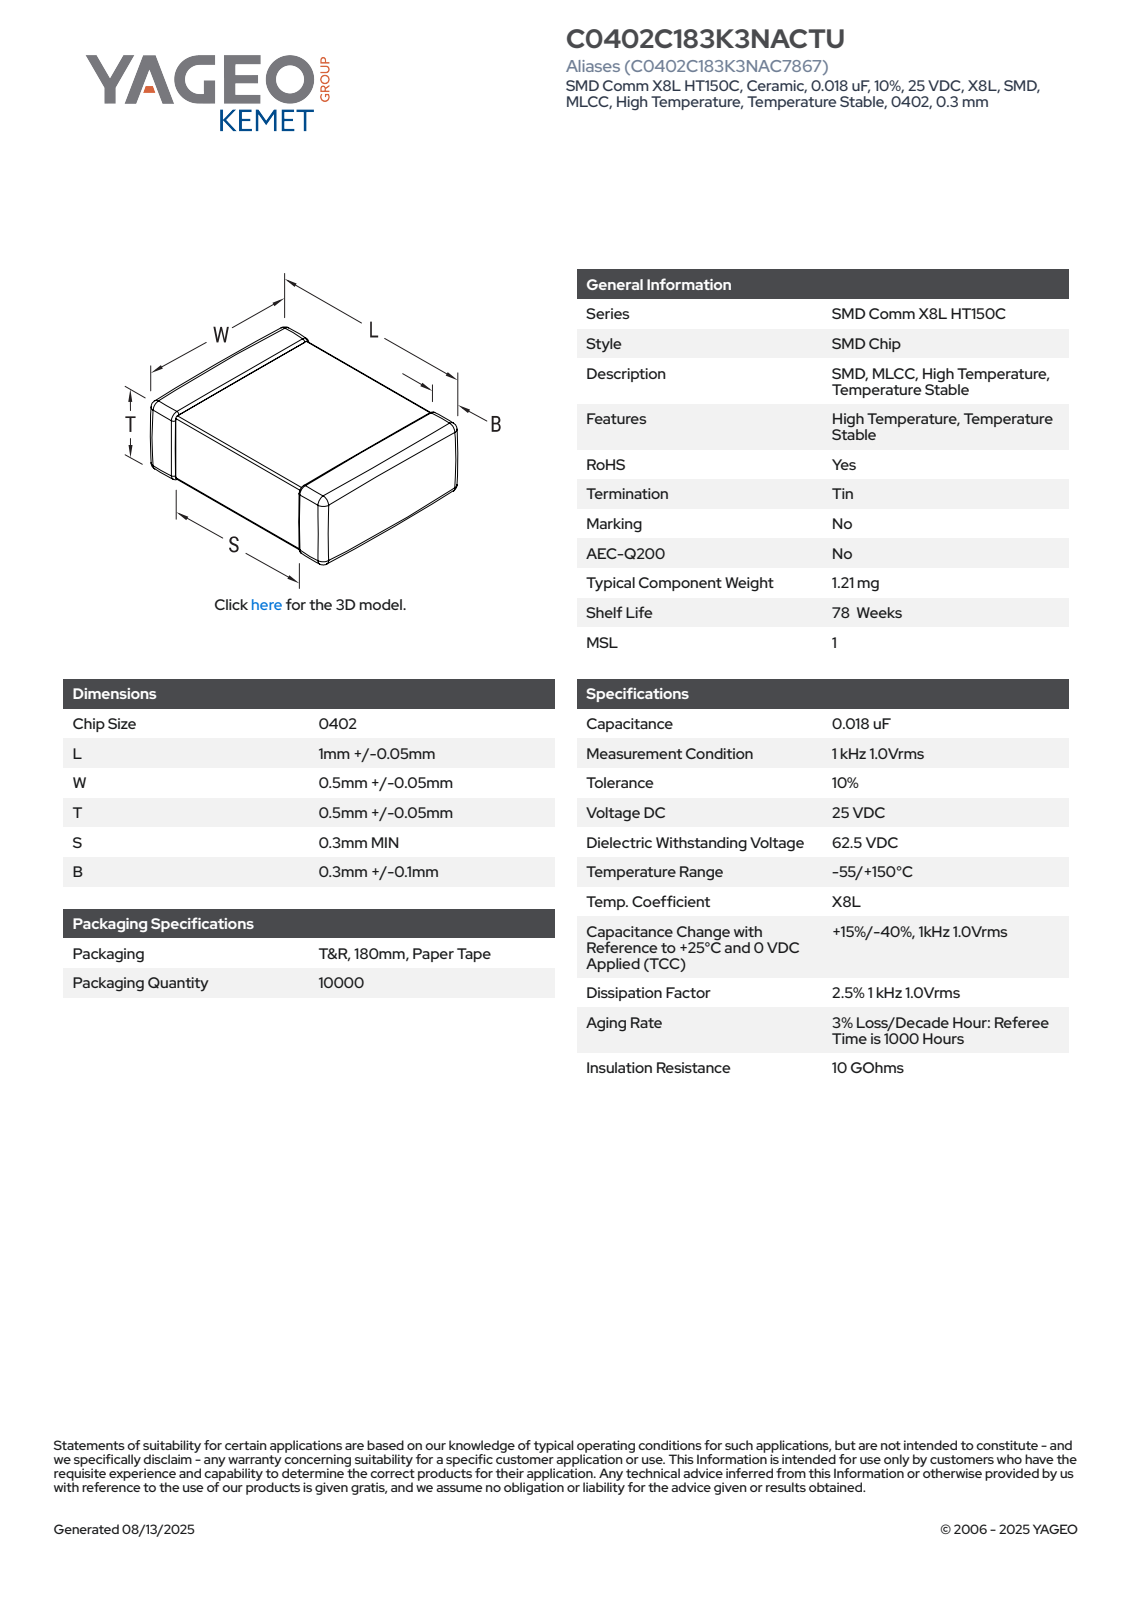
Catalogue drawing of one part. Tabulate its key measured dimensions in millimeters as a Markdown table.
| quantity | value |
| --- | --- |
| part name | CCS_CCSTD_0402_L1.05W0.55S0.5T0.55B0.3 |
| STEP written by | SolidWorks 2021 (AUTOMOTIVE_DESIGN) |
| units | millimeters |
| bodies | 4 solids, 125 faces (71 planar, 38 cylindrical, 16 other) |
| overall size | 1.05 × 0.55 × 0.55 |
| volume | 0.311 mm³ |
| surface area | 3 mm² |
| main face-to-face distances | 0.55, 0.54, 1.05, 0.53, 0.49, 0.56, 0.57, 0.48, 0.5, 0.52 |
